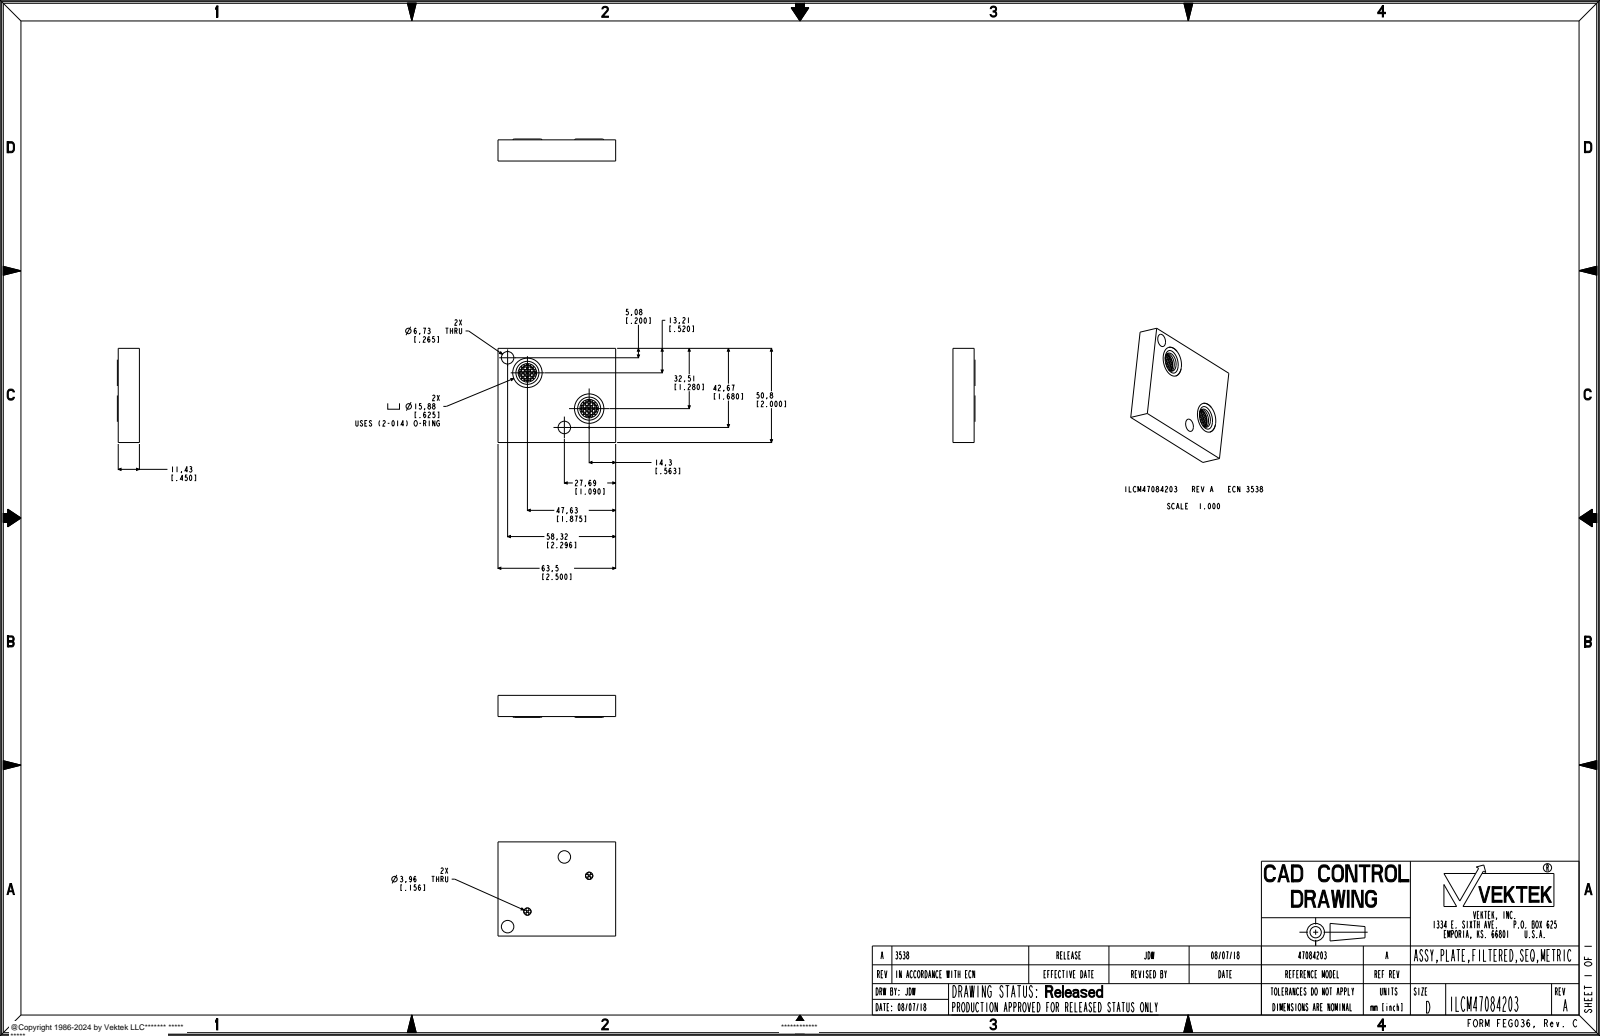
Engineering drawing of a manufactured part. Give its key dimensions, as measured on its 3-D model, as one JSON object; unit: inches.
{"part_name": "ILCM47084203", "step_written_by": "PRO/ENGINEER BY PARAMETRIC TECHNOLOGY CORPORATION, 2013320 (AUTOMOTIVE_DESIGN)", "units": "inches", "bodies": {"solids": 3, "faces": 322, "planar": 30, "cylindrical": 284, "other": 8}, "overall_size": [2.5, 2, 0.468], "volume_in3": 2.103, "surface_area_in2": 17.04, "round_holes": [[0.062, 32], [0.156, 2], [0.265, 2], [0.392, 2], [0.411, 2], [0.625, 2]], "partial_cylinders_radius": [[0.031, 32], [0.187, 2]], "face_to_face_distances": [0.45, 2, 2.5, 0.398, 0.052, 0.031, 0.196, 0.082, 0.316, 0.368], "hole_center_spacings": [0.094, 0.133, 0.21, 0.149, 0.067, 0.105, 0.148, 0.24]}
